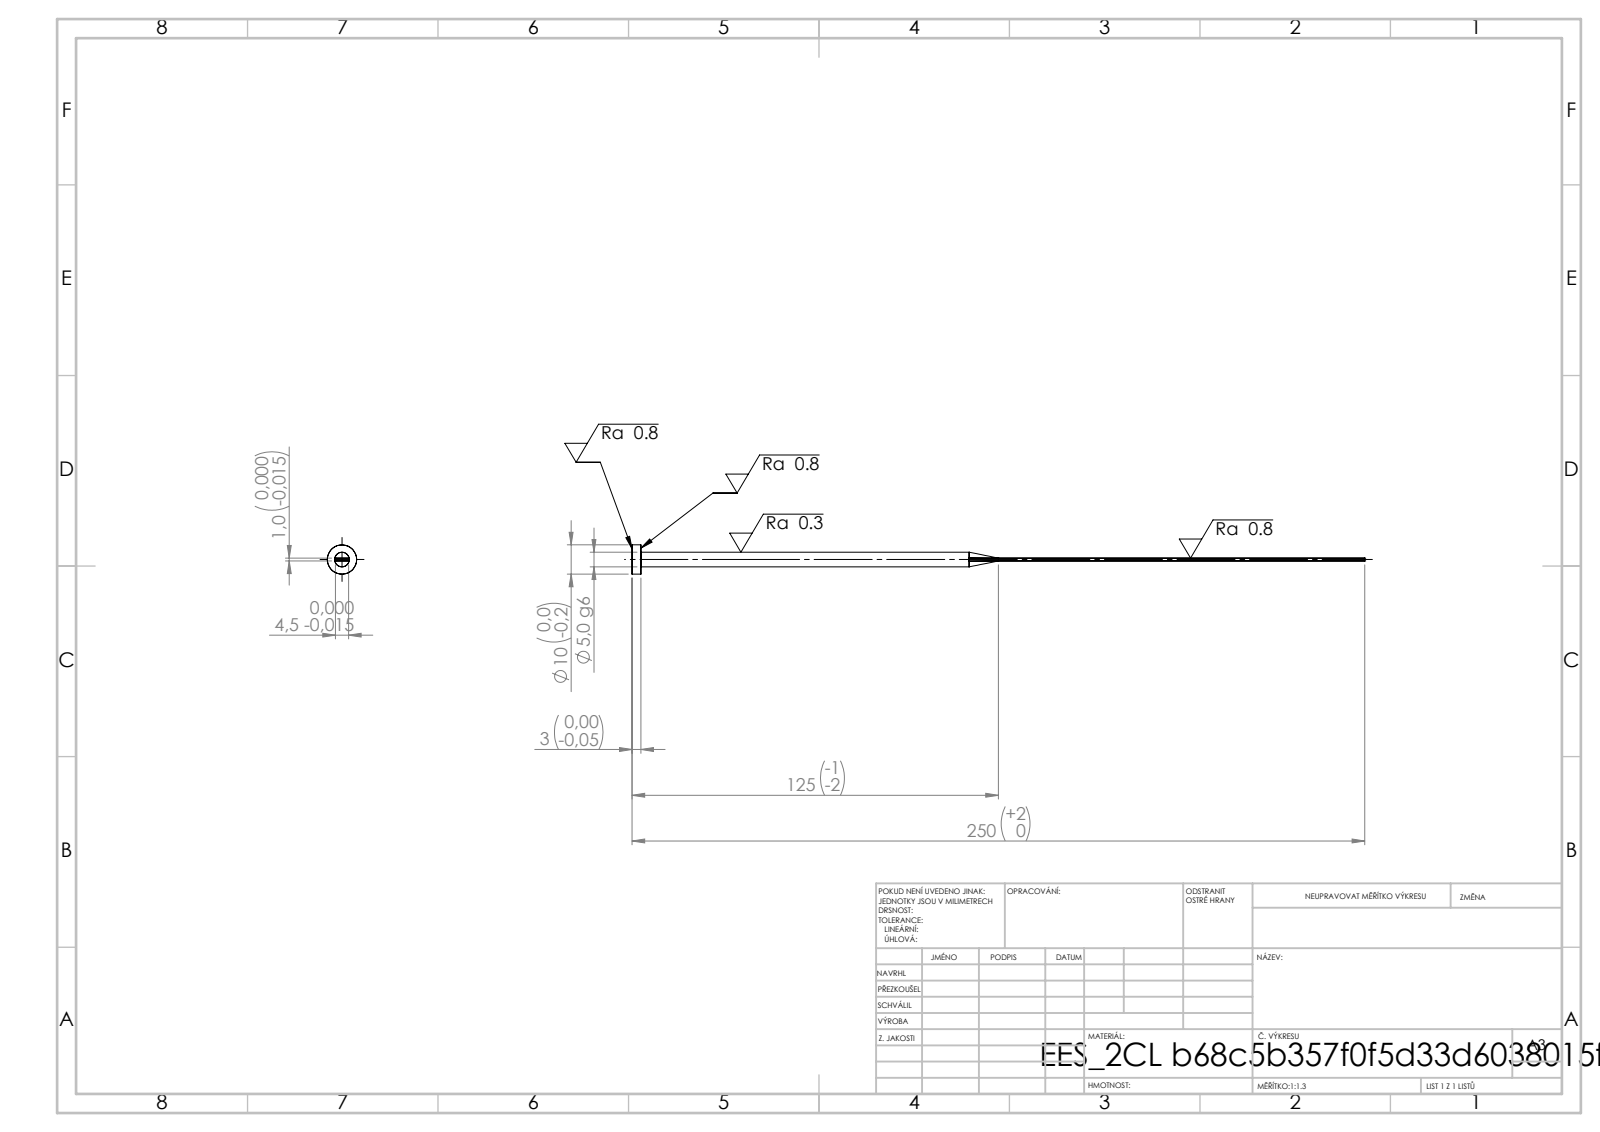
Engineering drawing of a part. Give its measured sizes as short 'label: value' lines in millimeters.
written by: SolidWorks 2019 (CONFIG_CONTROL_DESIGN)
unit: mm
bodies: 1 solid, 15 faces (7 planar, 4 cylindrical, 4 other)
size: 250 × 10 × 10
volume: 3 112 mm³; area: 3 499 mm²
bosses: 1× ⌀10, 1× ⌀5
face distances: 1, 4.5, 3, 250, 247
